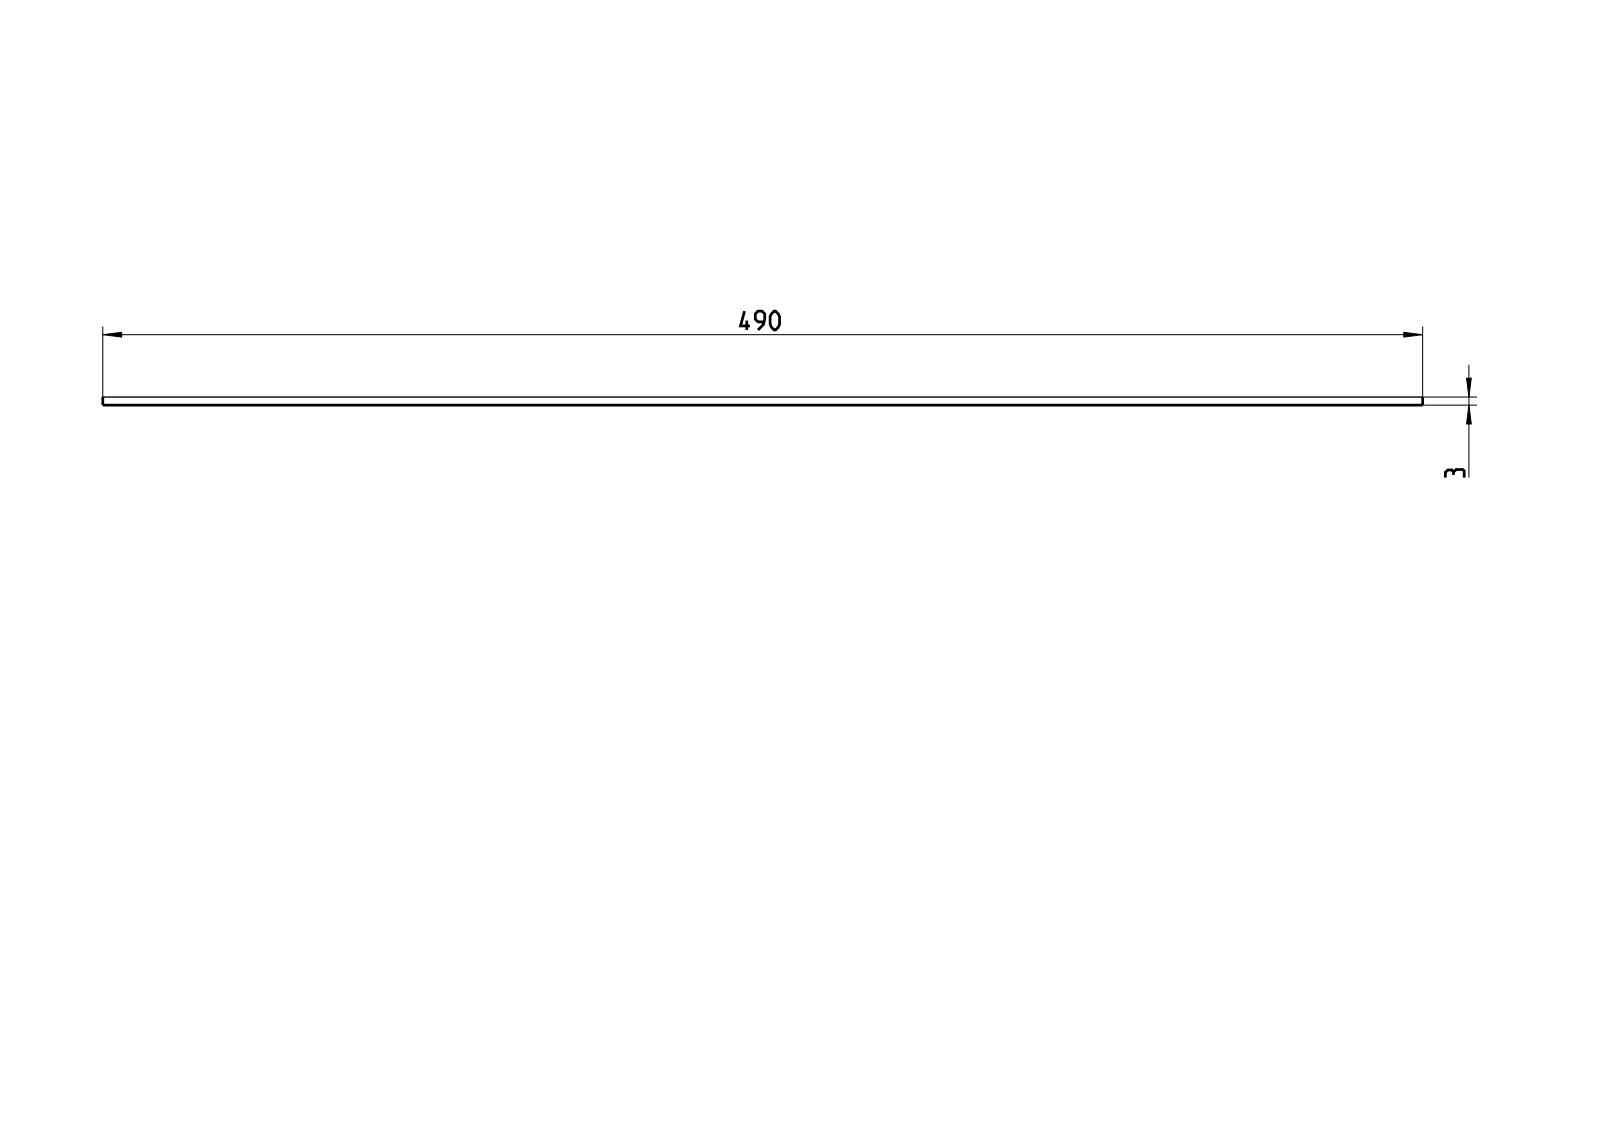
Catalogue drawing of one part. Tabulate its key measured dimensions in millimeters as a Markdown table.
| quantity | value |
| --- | --- |
| part name | T-01188; BKG5002BL2_ASM |
| STEP written by | CREO PARAMETRIC BY PTC INC, 2022024 (AUTOMOTIVE_DESIGN) |
| units | millimeters |
| bodies | 1 solid, 6 faces (6 planar, 0 cylindrical, 0 other) |
| overall size | 999 × 490 × 3 |
| volume | 1 469 000 mm³ |
| surface area | 987 954 mm² |
| main face-to-face distances | 3, 490, 999 |
